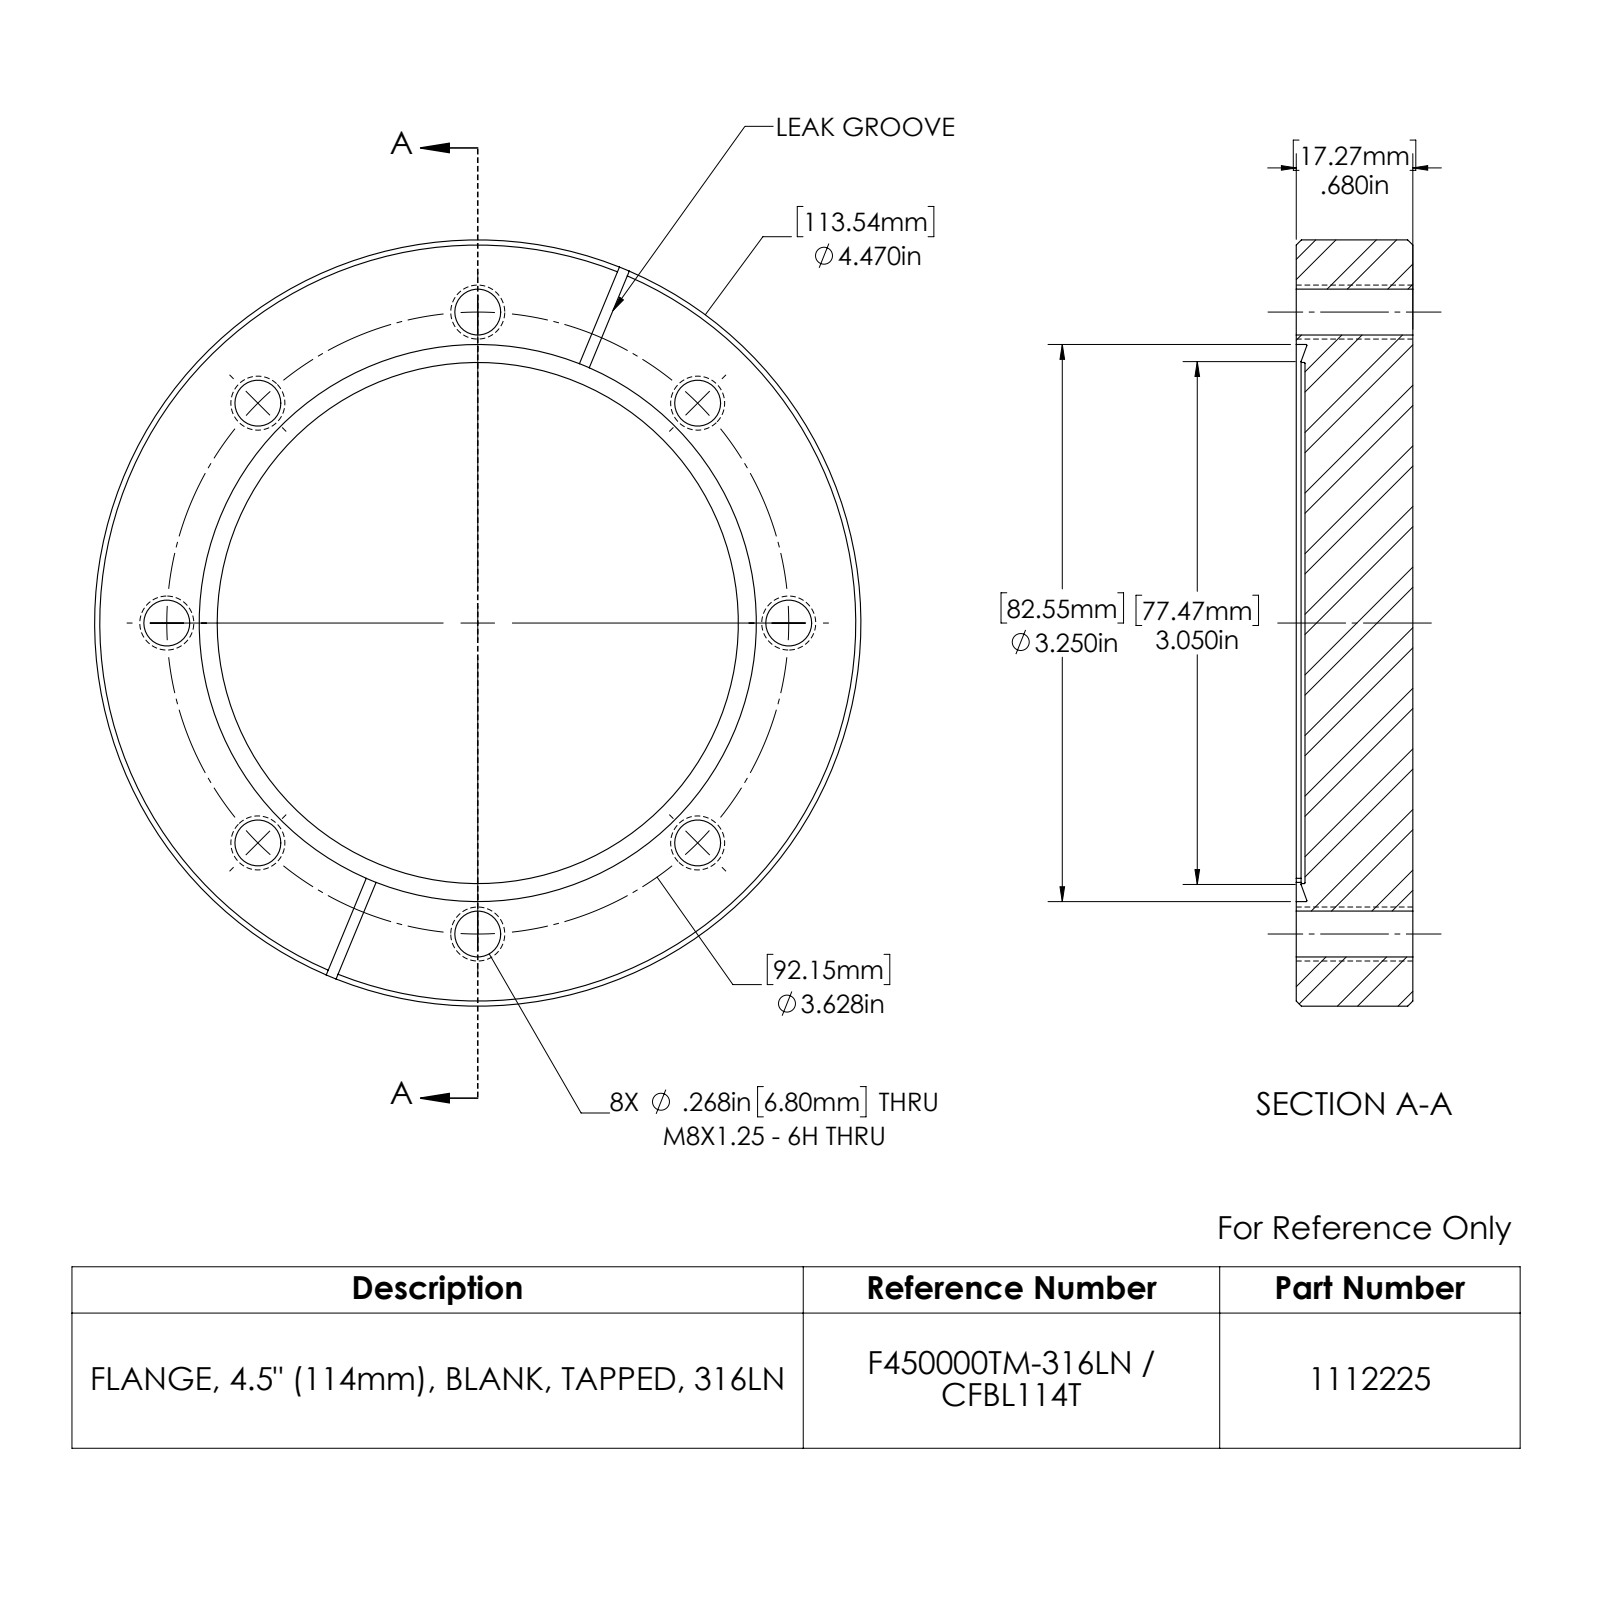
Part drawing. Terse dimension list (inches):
name: 1112225_A
written by: SolidWorks 2022 (CONFIG_CONTROL_DESIGN)
unit: in
bodies: 1 solid, 45 faces (10 planar, 22 cylindrical, 13 other)
size: 4.47 × 4.47 × 0.68
volume: 9.932 in³; area: 45.07 in²
holes: 8× ⌀0.268, 1× ⌀3.04, 1× ⌀3.25
bosses: 1× ⌀4.47
face distances: 0.629, 0.051, 0.68, 0.05, 0.63, 0.062, 0.061, 0.062, 0.063
hole spacings: 1.389, 1.814, 3.352, 2.565, 2.566, 3.628, 3.628
